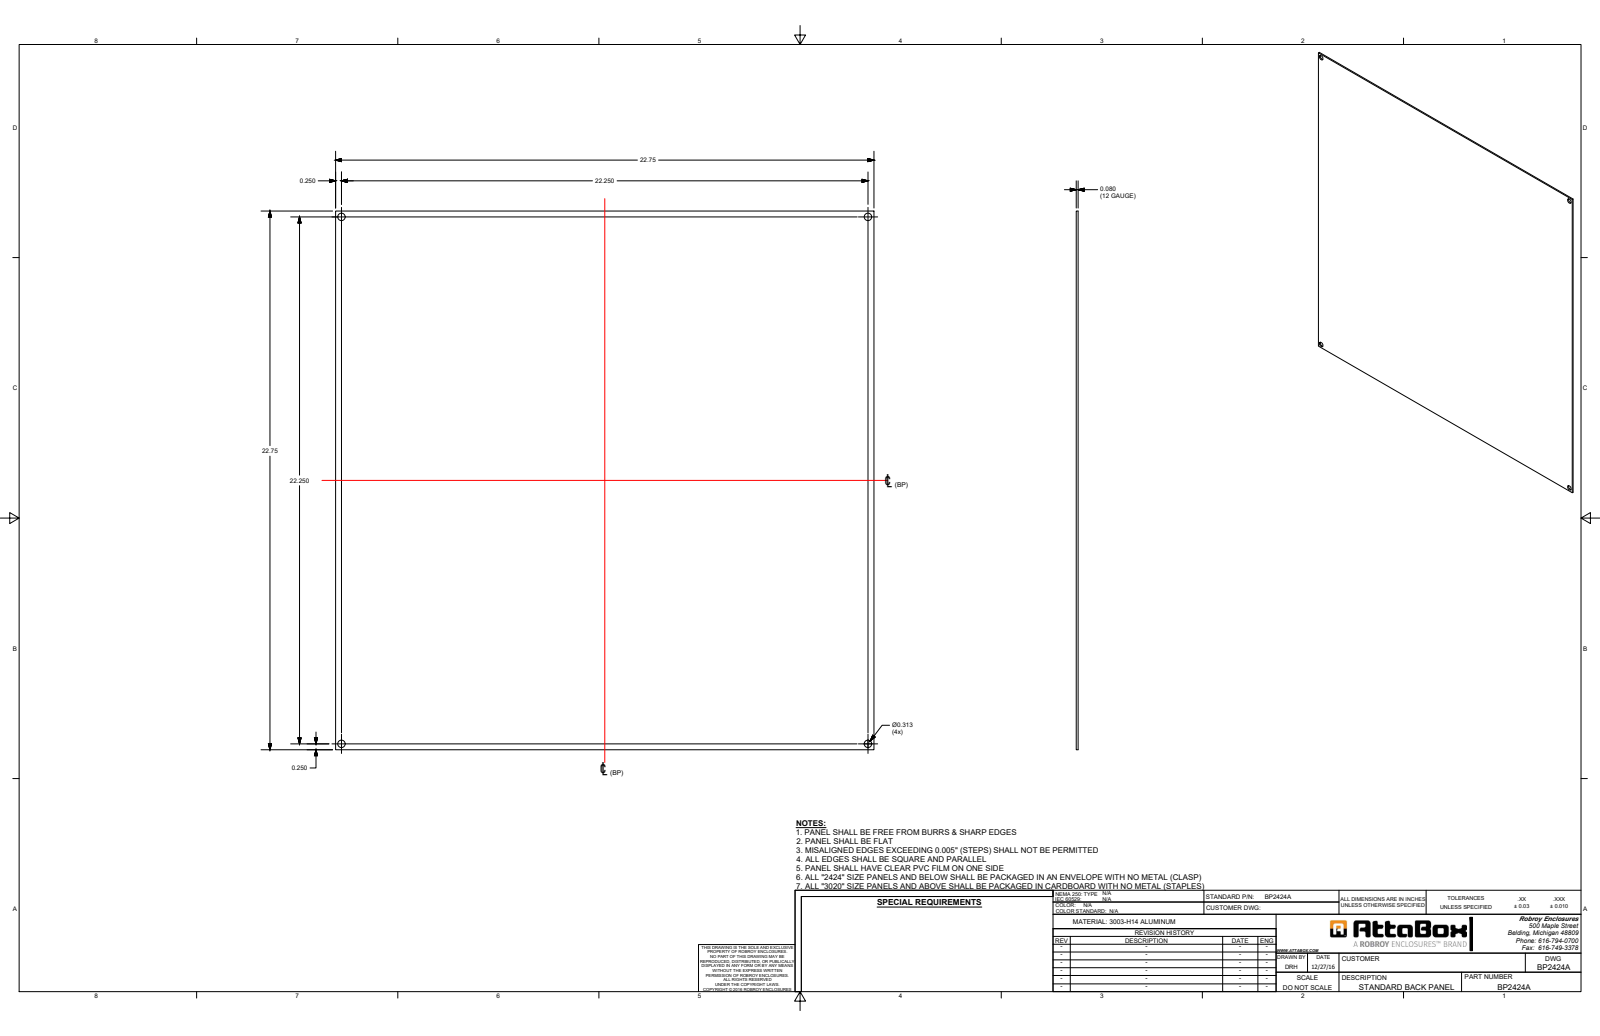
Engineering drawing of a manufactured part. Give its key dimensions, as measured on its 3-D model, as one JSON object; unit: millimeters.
{"part_name": "BP2424A", "step_written_by": "SolidWorks 2023 (AUTOMOTIVE_DESIGN)", "units": "millimeters", "bodies": {"solids": 1, "faces": 10, "planar": 6, "cylindrical": 4, "other": 0}, "overall_size": [577.9, 577.9, 2], "volume_mm3": 678100, "surface_area_mm2": 672300, "round_holes": [[8, 4]], "face_to_face_distances": [2, 577.9], "hole_center_spacings": [565.2, 799.2]}
